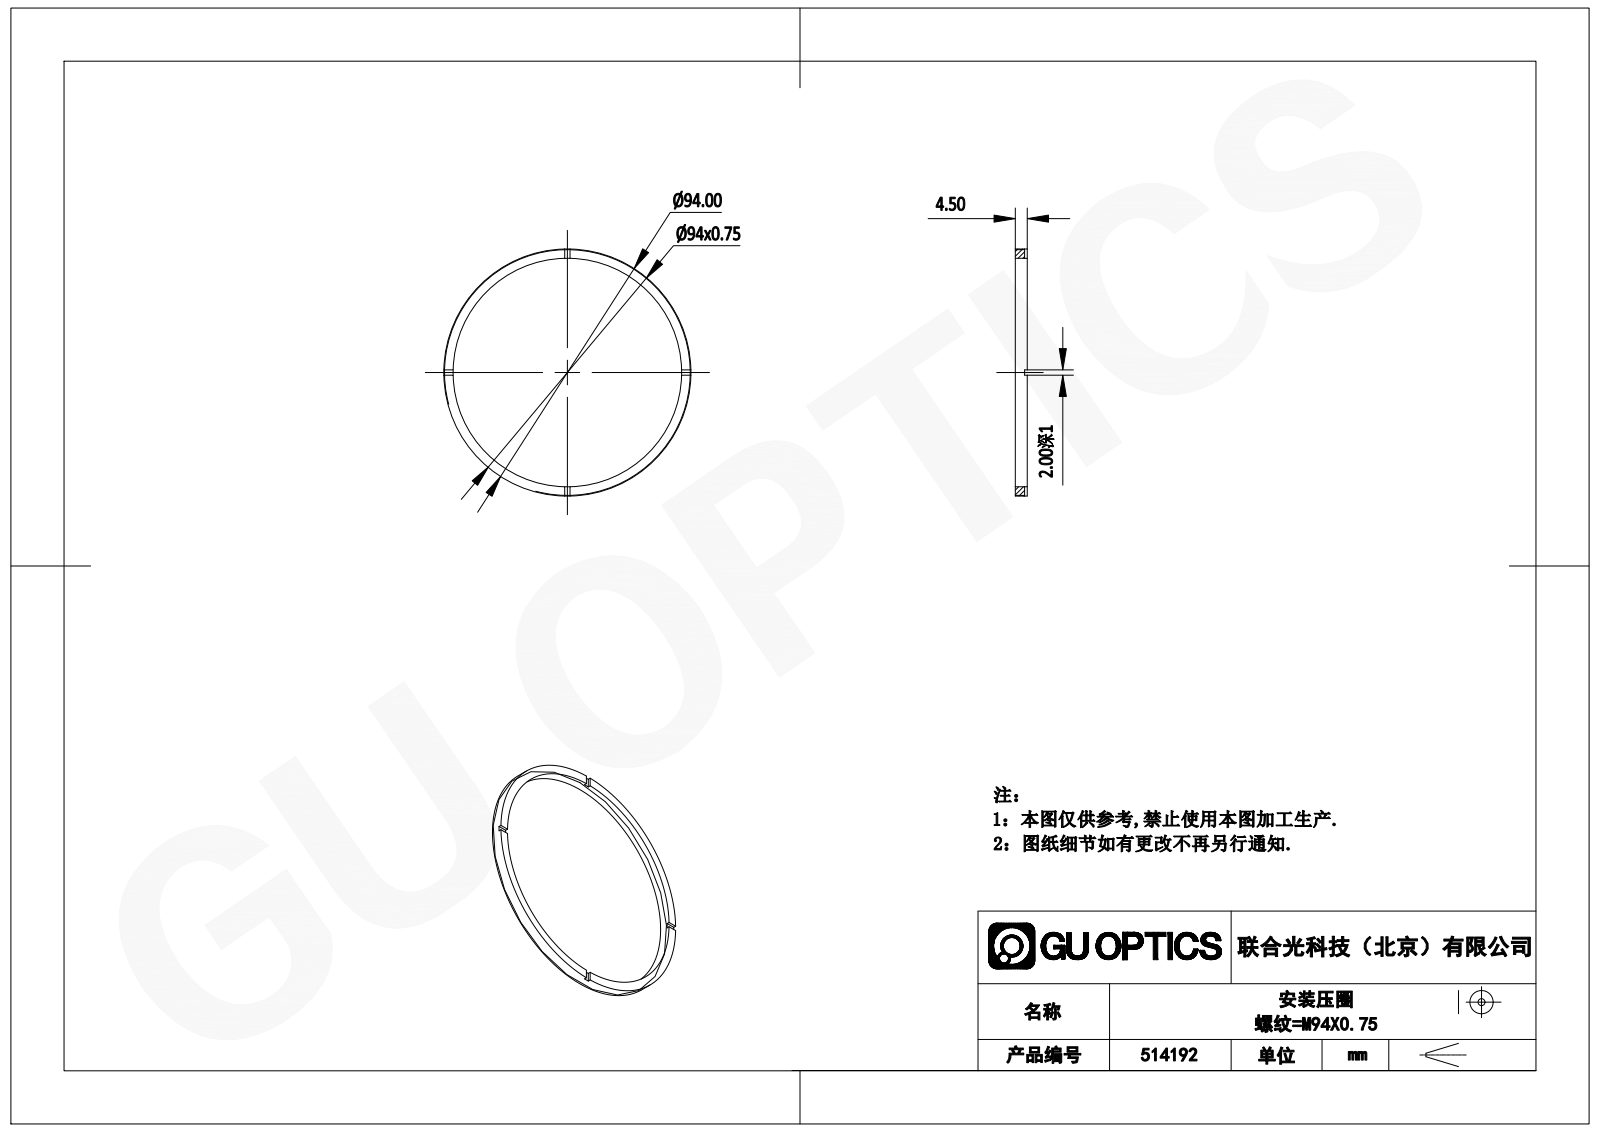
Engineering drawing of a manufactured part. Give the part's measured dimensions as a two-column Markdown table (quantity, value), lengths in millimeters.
| quantity | value |
| --- | --- |
| part name | 514192 |
| STEP written by | SolidWorks 2020 (CONFIG_CONTROL_DESIGN) |
| units | millimeters |
| bodies | 1 solid, 21 faces (17 planar, 4 cylindrical, 0 other) |
| overall size | 94 × 94 × 4.5 |
| volume | 4 450 mm³ |
| surface area | 4 561 mm² |
| round holes (diameter × count) | 87 × 1 |
| round bosses / shafts (diameter × count) | 94 × 1 |
| main face-to-face distances | 4.5, 3.5, 1, 2 |
